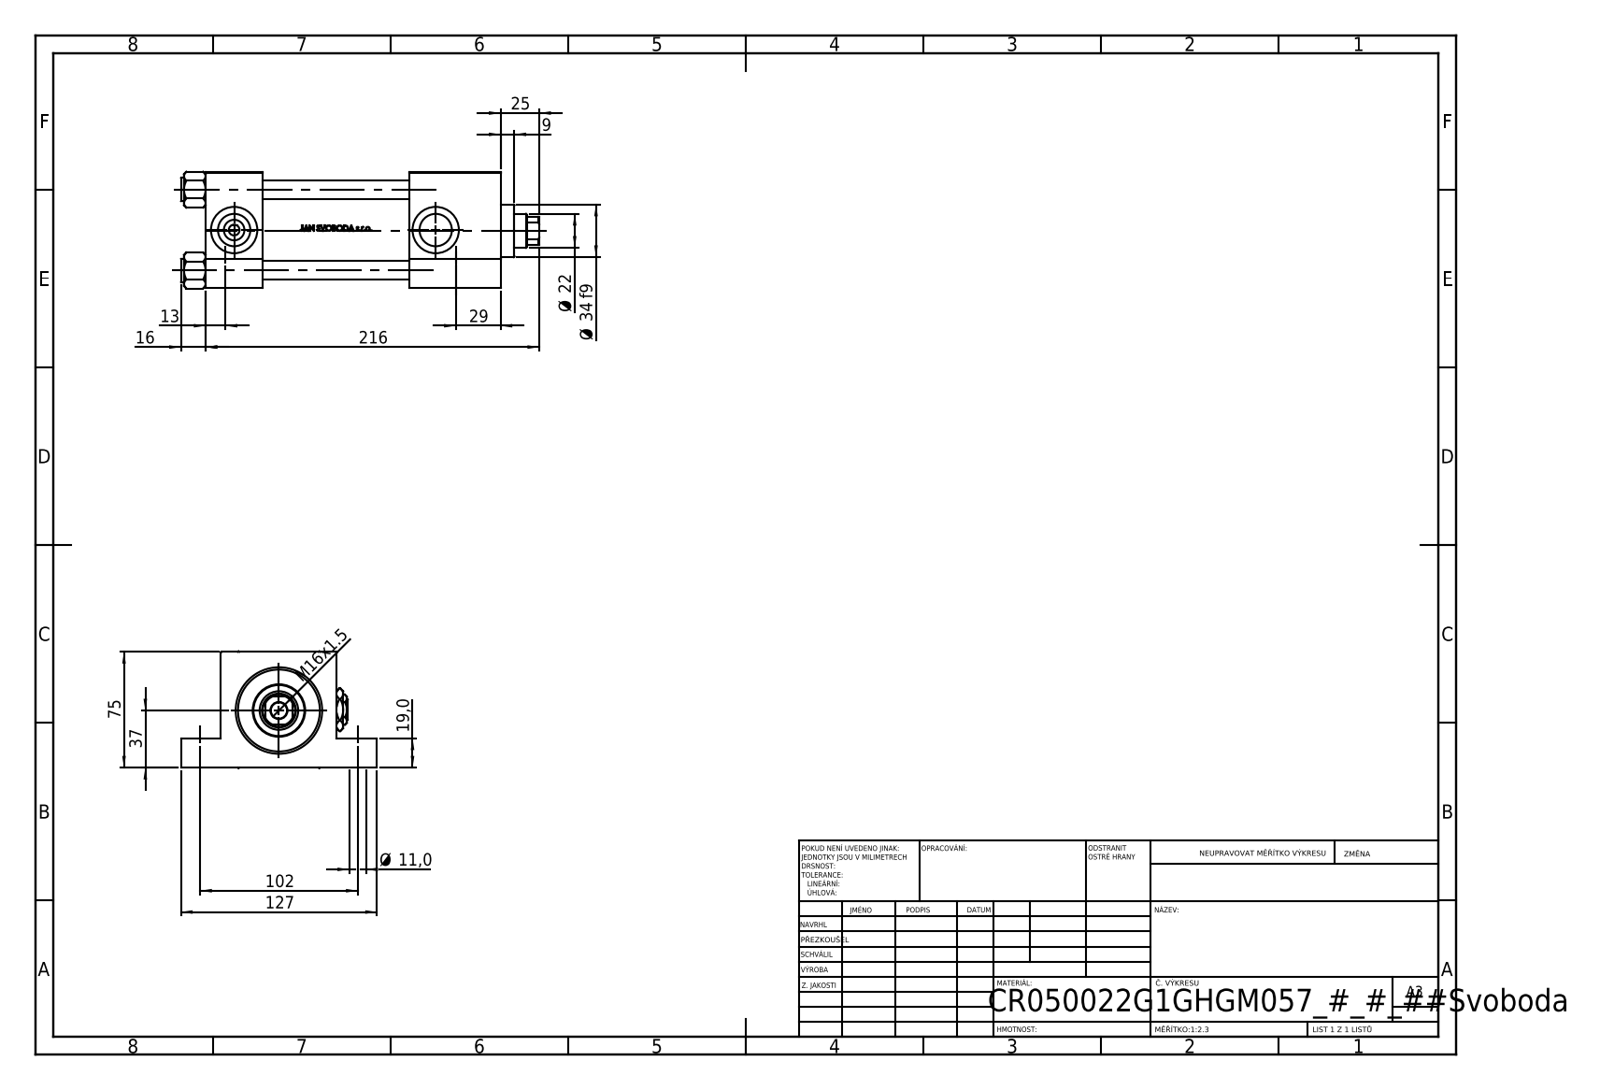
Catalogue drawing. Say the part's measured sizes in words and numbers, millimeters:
The part is named "V215CR_G_TYCINKA; V215_VC_A; NUT_M5_G; V215CR_VCP_G (+2 more)". Its 3-D file was written by "SolidWorks 2019 (CONFIG_CONTROL_DESIGN)". It is 12 solids with 1134 faces: 454 planar, 128 cylindrical and 552 other. Overall it measures 232 by 127 by 75.54 millimeters. Its volume is 801 688 cubic millimeters and its surface area 181 762 square millimeters. Round holes: 4 of diameter 11, 4 of diameter 12, 2 of diameter 7, 2 of diameter 20.96, 2 of diameter 30, 1 of diameter 10.5, 1 of diameter 22, 1 of diameter 25, 1 of diameter 41, 1 of diameter 50, 1 of diameter 53. Round bosses or shafts: 4 of diameter 15, 1 of diameter 56, 1 of diameter 34. Partial cylindrical surfaces (rounded edges, fillets, slot ends): 1 of radius 10.5. The main face-to-face distances are 75, 37, 191, 154, 19, 56, 132, 95, 59, 26. The hole center spacings are 52.3, 36.63, 37.34, 73.96, 102, 149, 180.57, 130.5.
